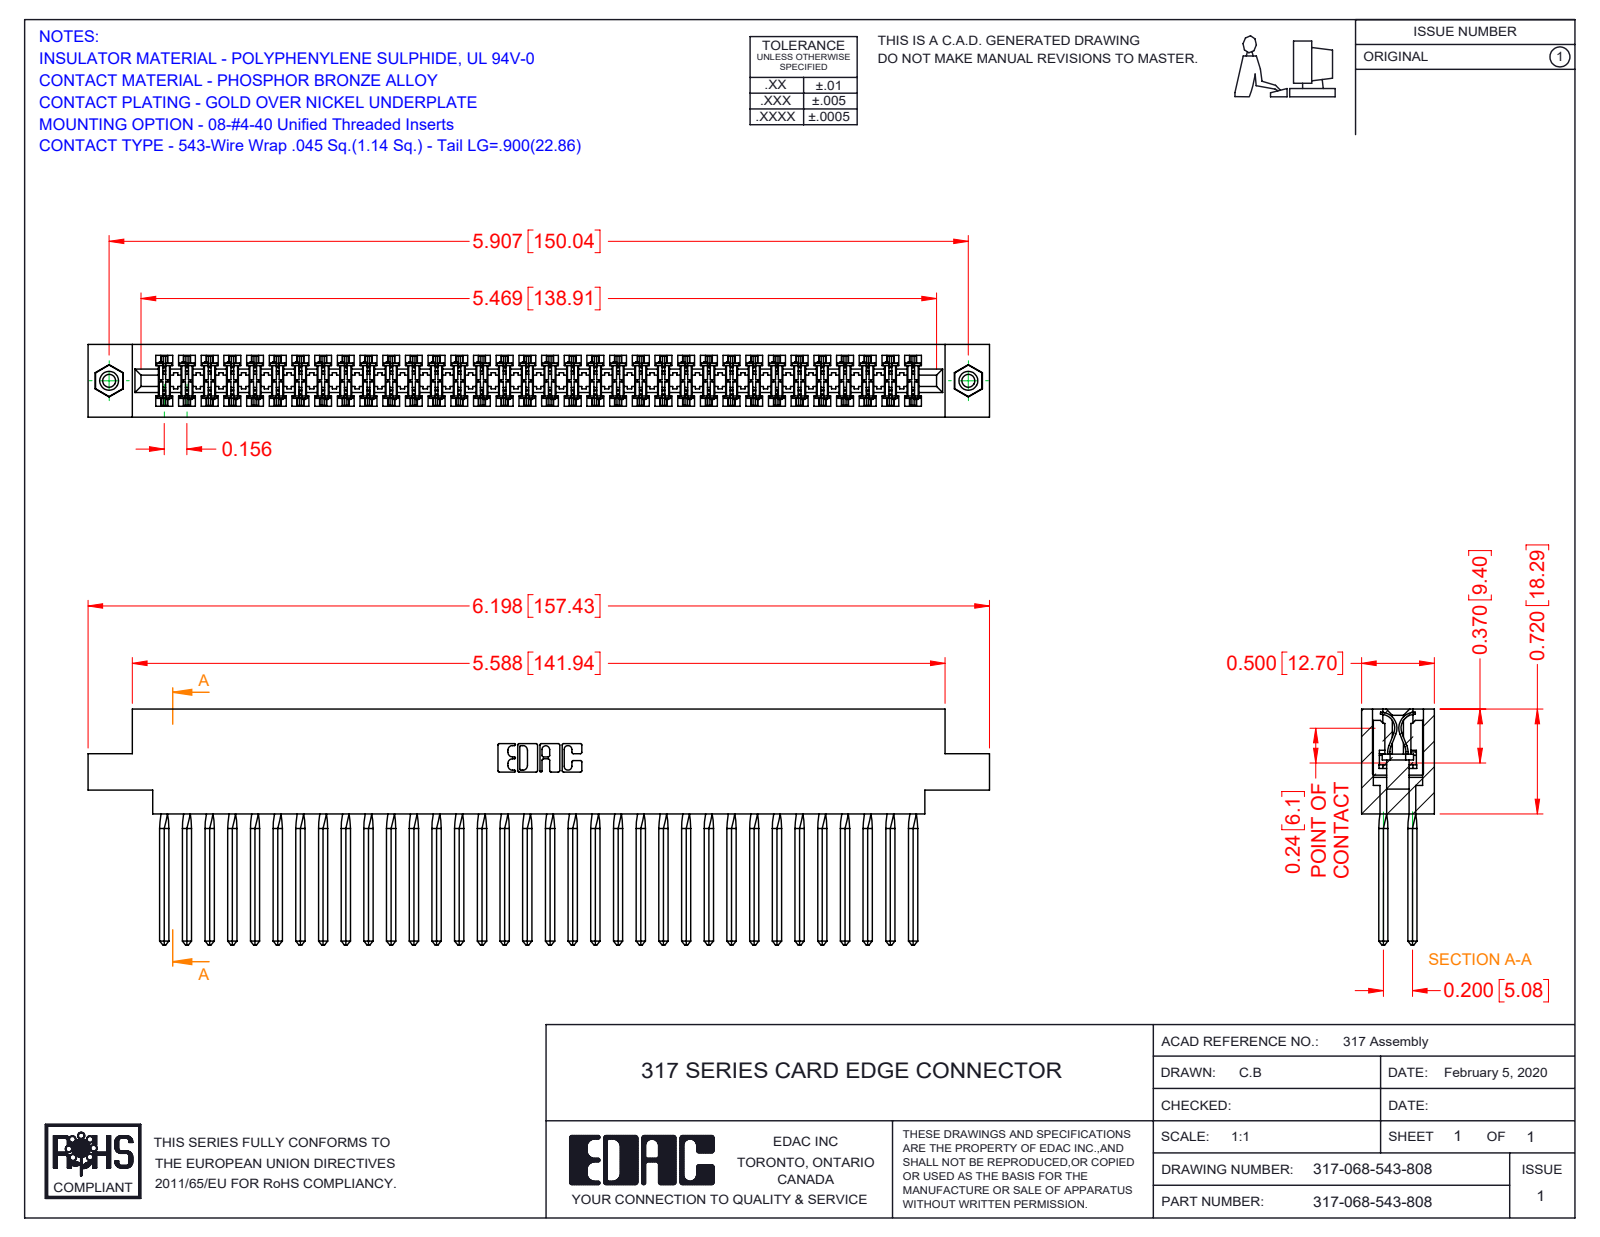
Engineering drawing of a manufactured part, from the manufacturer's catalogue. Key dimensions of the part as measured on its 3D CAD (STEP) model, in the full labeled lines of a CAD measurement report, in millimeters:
Part name (STEP PRODUCT): 317-068-543-878; 345-250-001_345-250-003-102; 317-290-001_543; 317 Part_.156 Dia - TI
STEP written by: SolidWorks 2016 (CONFIG_CONTROL_DESIGN)
Units: millimetres
Bodies: 71 solids, 6214 faces (5054 planar, 872 cylindrical, 288 other)
Overall size (bounding box): 157.4 × 41.1 × 12.7
Volume: 26 480 mm³ · Surface area: 39 880 mm²
Round holes (diameter × count): ⌀2.3 ×2, ⌀3.2 ×2, ⌀4 ×2
Round bosses / shafts (diameter × count): ⌀3.9 ×2
Partial cylindrical surfaces — rounded edges, fillets, slot ends (radius × count): R0.4 ×136, R0.3 ×22, R0.2 ×6, R0.8 ×6, R0.7 ×3, R2.4 ×2, R2.5 ×2, R2.8 ×2
Main face-to-face distances: 12.7, 1.9, 10.8, 8.9, 2.8, 5, 2.4, 5.1, 2.9, 3.3
Hole centre spacings: 150
